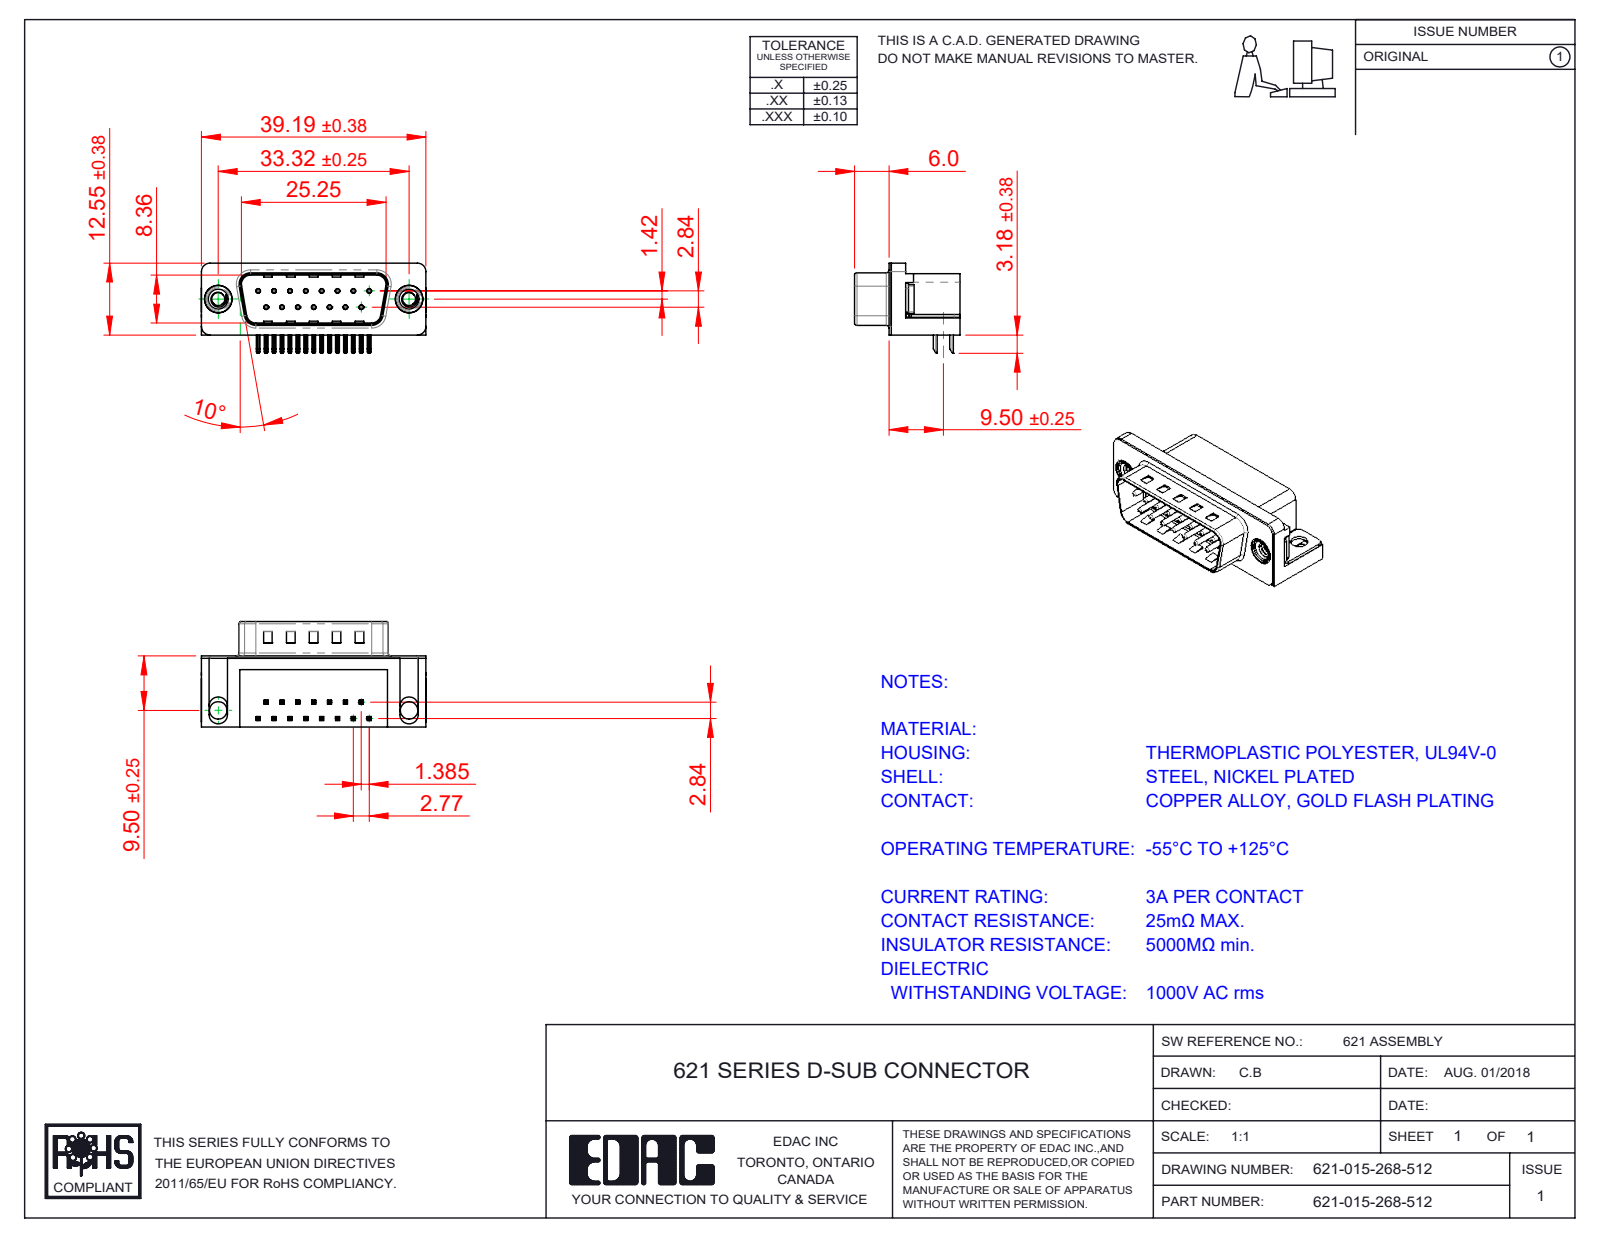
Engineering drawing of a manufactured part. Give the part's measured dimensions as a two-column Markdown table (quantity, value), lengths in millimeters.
| quantity | value |
| --- | --- |
| part name | 621 Thru Hole Board Mount; 621 4-40 Threaded Rivet; 621 Contact Top; 621 Contact Bottom (+3 more) |
| STEP written by | SolidWorks 2016 (CONFIG_CONTROL_DESIGN) |
| units | millimeters |
| bodies | 21 solids, 1475 faces (891 planar, 445 cylindrical, 139 other) |
| overall size | 39.22 × 18.4 × 15.73 |
| volume | 4 414 mm³ |
| surface area | 5 637 mm² |
| round holes (diameter × count) | 0.35 × 15, 0.8 × 15, 2.26 × 2, 3.05 × 2, 4 × 2, 4.8 × 2, 5 × 2 |
| round bosses / shafts (diameter × count) | 0.75 × 15, 4.9 × 2, 4.75 × 2, 3.9 × 2 |
| partial cylindrical surfaces (radius × count) | 0.25 × 68, 0.12 × 30, 1 × 16, 0.5 × 9, 1.6 × 8, 1.5 × 6, 0.9 × 4, 2 × 4 |
| main face-to-face distances | 0.4, 12, 10.35, 2.1, 10.46, 12.4, 1.7, 10.86, 8.76, 2.9 |
| hole center spacings | 3.16, 2.77, 5.54, 8.31, 11.08, 5.03, 5.04, 7.48 |
